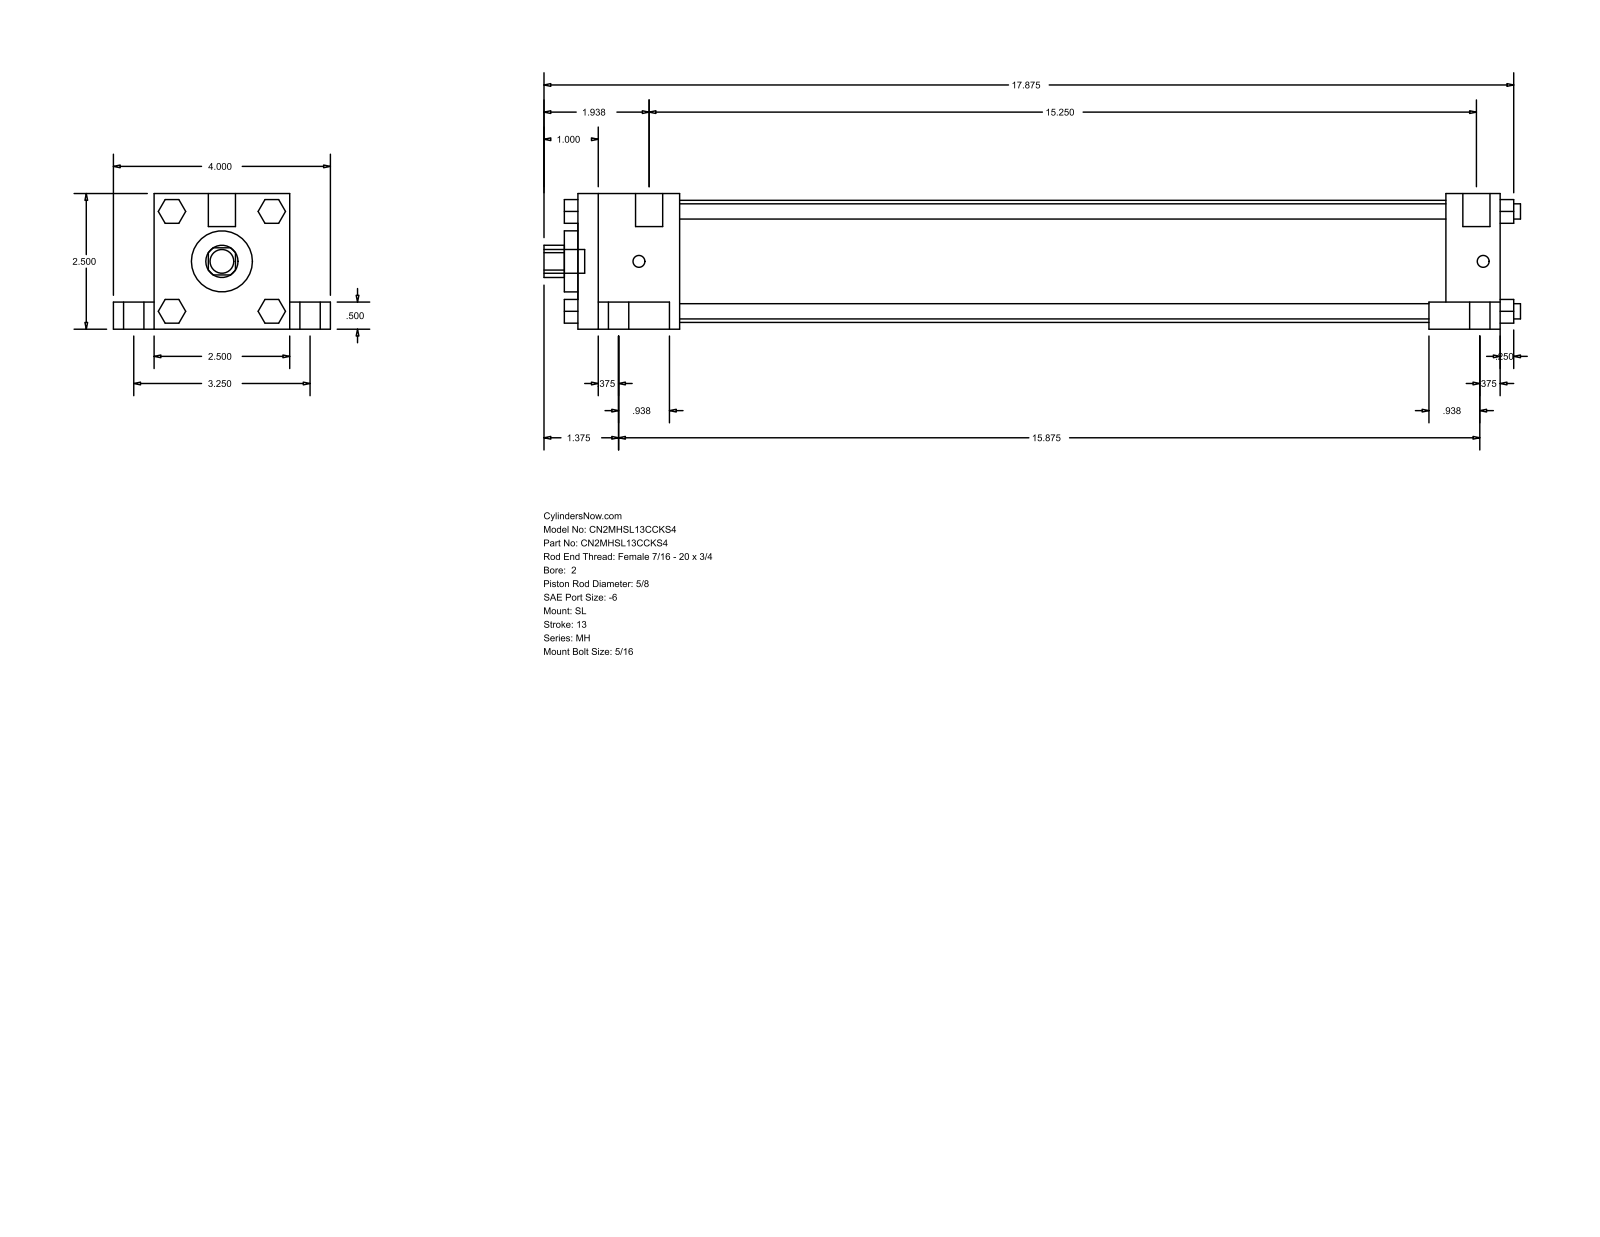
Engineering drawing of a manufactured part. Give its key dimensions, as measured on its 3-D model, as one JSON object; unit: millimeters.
{"part_name": "MH_SL__0200_0.625", "step_written_by": "GSSL Pune (CONFIG_CONTROL_DESIGN)", "units": "millimeters", "bodies": {"solids": 0, "faces": 148, "planar": 112, "cylindrical": 36, "other": 0}, "overall_size": [457.2, 101.6, 63.5], "round_holes": [[15.88, 1], [28.57, 1], [57.15, 1]], "round_bosses_or_shafts": [[15.88, 4], [9.53, 4], [7.14, 4], [5.56, 4], [12.7, 2], [11.11, 1]], "partial_cylinders_radius": [[7.54, 1]], "face_to_face_distances": [63.5, 431.8, 12.7, 19.05, 50.8, 82.55, 406.39, 25.41, 47.62, 358.77]}
